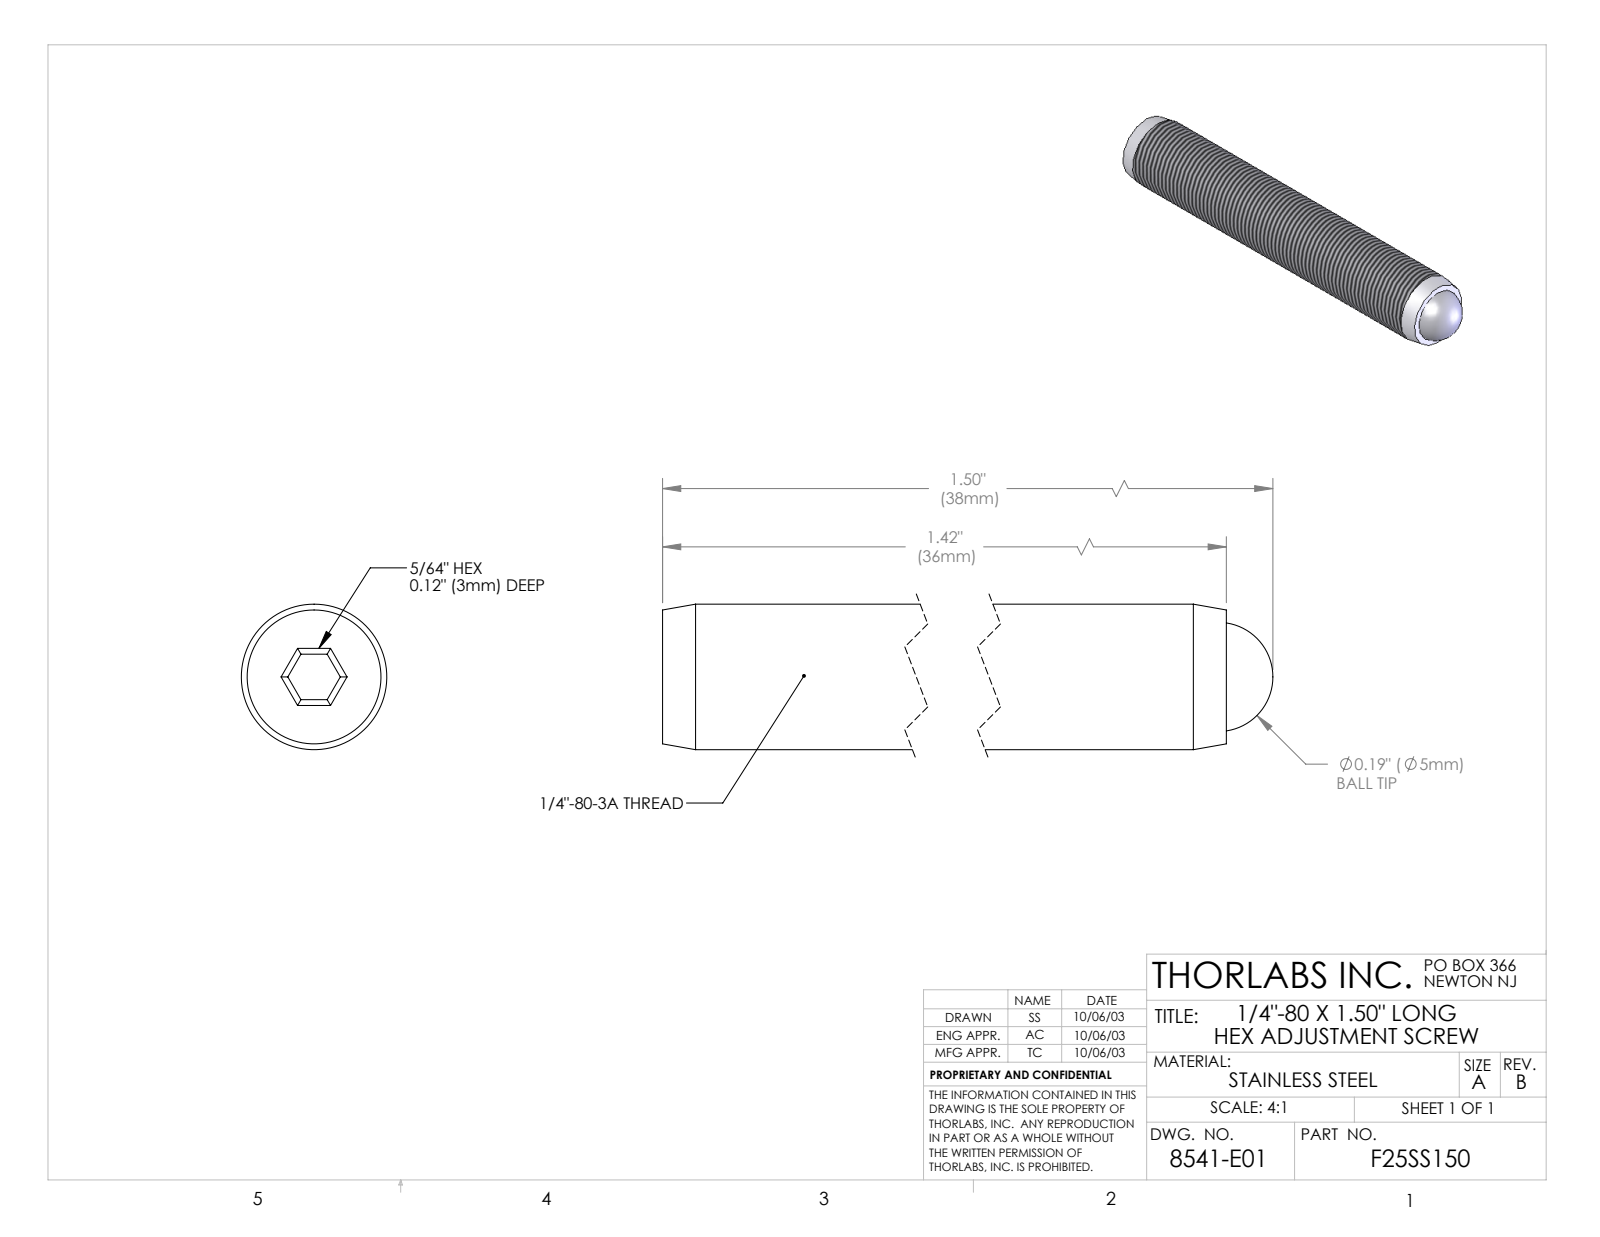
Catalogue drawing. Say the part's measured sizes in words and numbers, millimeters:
The part is named "8541-E0W". Its 3-D file was written by "SolidWorks 2007 (AUTOMOTIVE_DESIGN)". It is 2 solids with 29 faces: 15 planar, 4 cylindrical and 10 other. Overall it measures 38.1 by 6.35 by 6.35 millimeters. Its volume is 1 143 cubic millimeters and its surface area 890 square millimeters. Round holes: 1 of diameter 4.78. Round bosses or shafts: 1 of diameter 6.35. The main face-to-face distances are 36.07, 1.99, 3.05, 33.02, 1.98.
